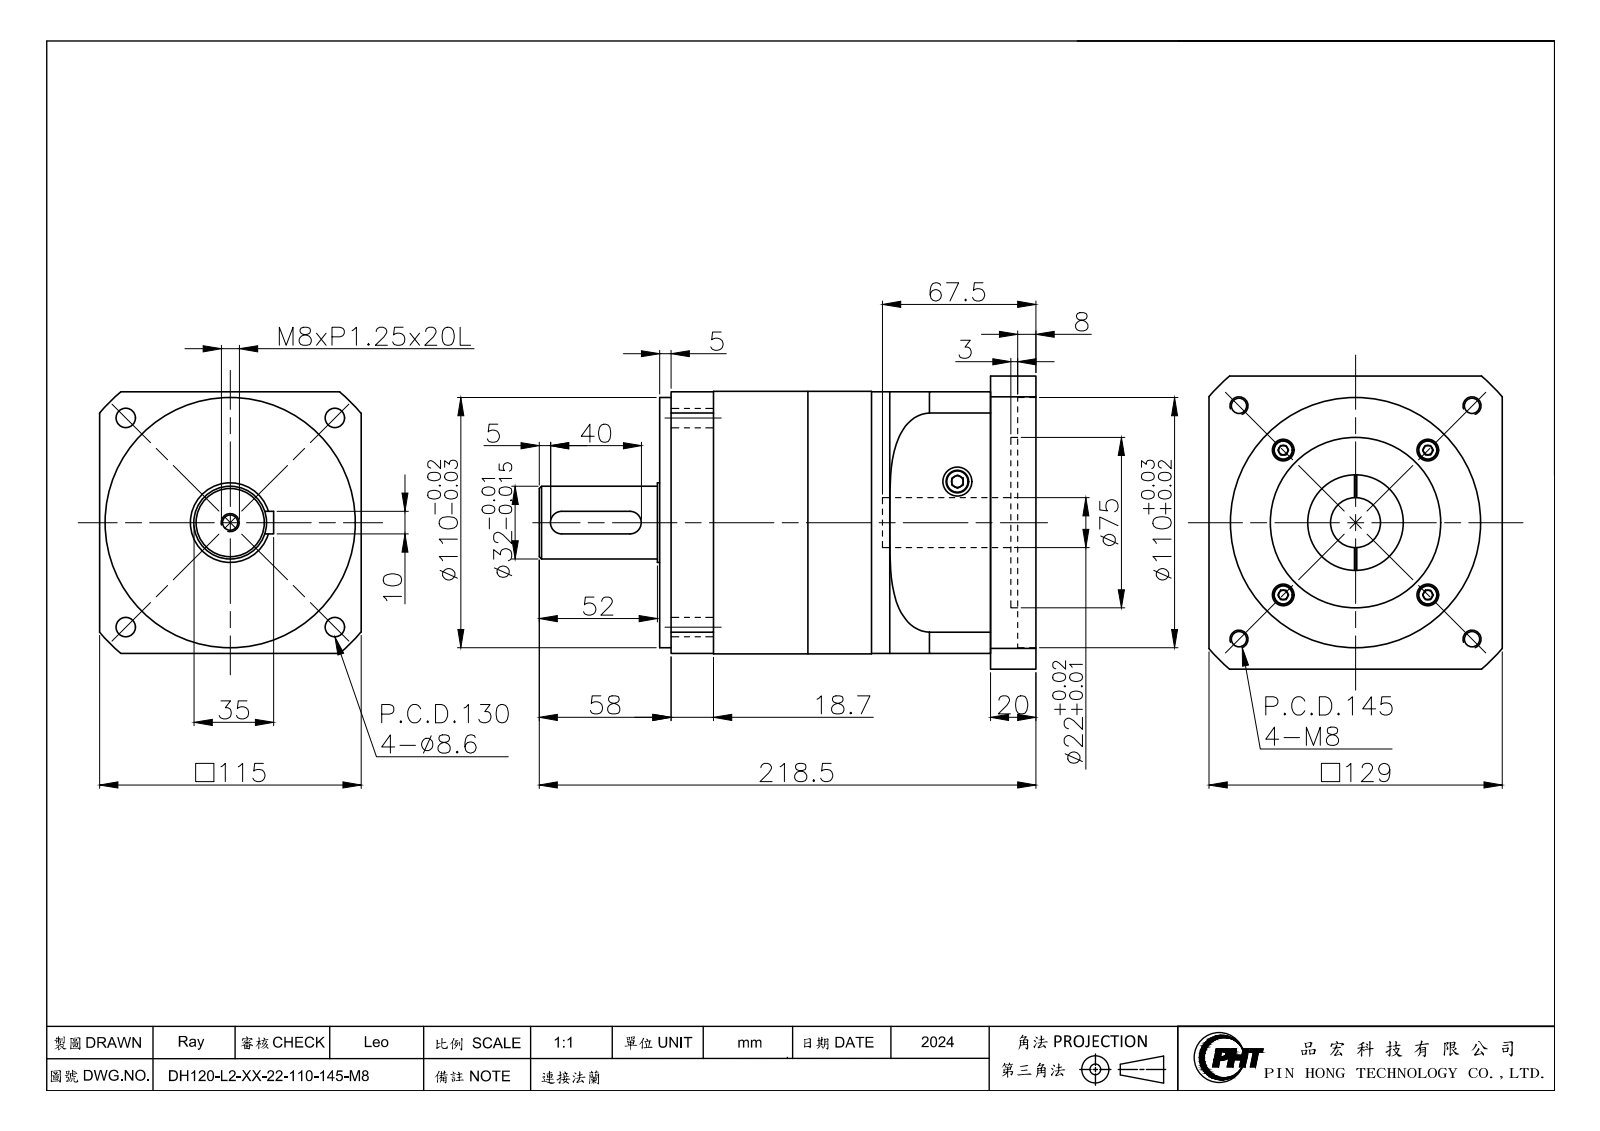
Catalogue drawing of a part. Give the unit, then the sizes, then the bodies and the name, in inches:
Units: inches
Overall size (bounding box): 8.602 × 5.079 × 5.079
Round holes (diameter × count): ⌀0.374 ×8, ⌀0.268 ×5, ⌀0.165 ×4, ⌀0.217 ×4, ⌀0.339 ×4, ⌀0.394 ×4, ⌀0.5 ×2, ⌀0.866 ×1, ⌀1.654 ×1, ⌀2.362 ×1, ⌀2.756 ×1, ⌀2.953 ×1
Round bosses / shafts (diameter × count): ⌀0.335 ×12, ⌀0.197 ×12, ⌀4.547 ×1, ⌀4.528 ×1, ⌀1.929 ×1, ⌀1.378 ×1, ⌀1.26 ×1
Partial cylindrical surfaces — rounded edges, fillets, slot ends (radius × count): R0.197 ×2, R2.953 ×1, R3.346 ×1
Main face-to-face distances: 1.634, 1.102, 2.736, 4.795, 3.161, 2.059, 4.528, 5.728, 3.669, 2.567
Hole centre spacings: 0.836, 1.008, 1.206, 2.126, 2.185, 2.628, 2.832, 3.007
Volume: 112.8 in³ · Surface area: 383 in²
Bodies: 20 solids, 395 faces (174 planar, 157 cylindrical, 64 other)
Part name (STEP PRODUCT): DH120-L2-XX-22-110-145-M8(連接法蘭)_2024
STEP written by: SolidWorks 2016 (CONFIG_CONTROL_DESIGN)
